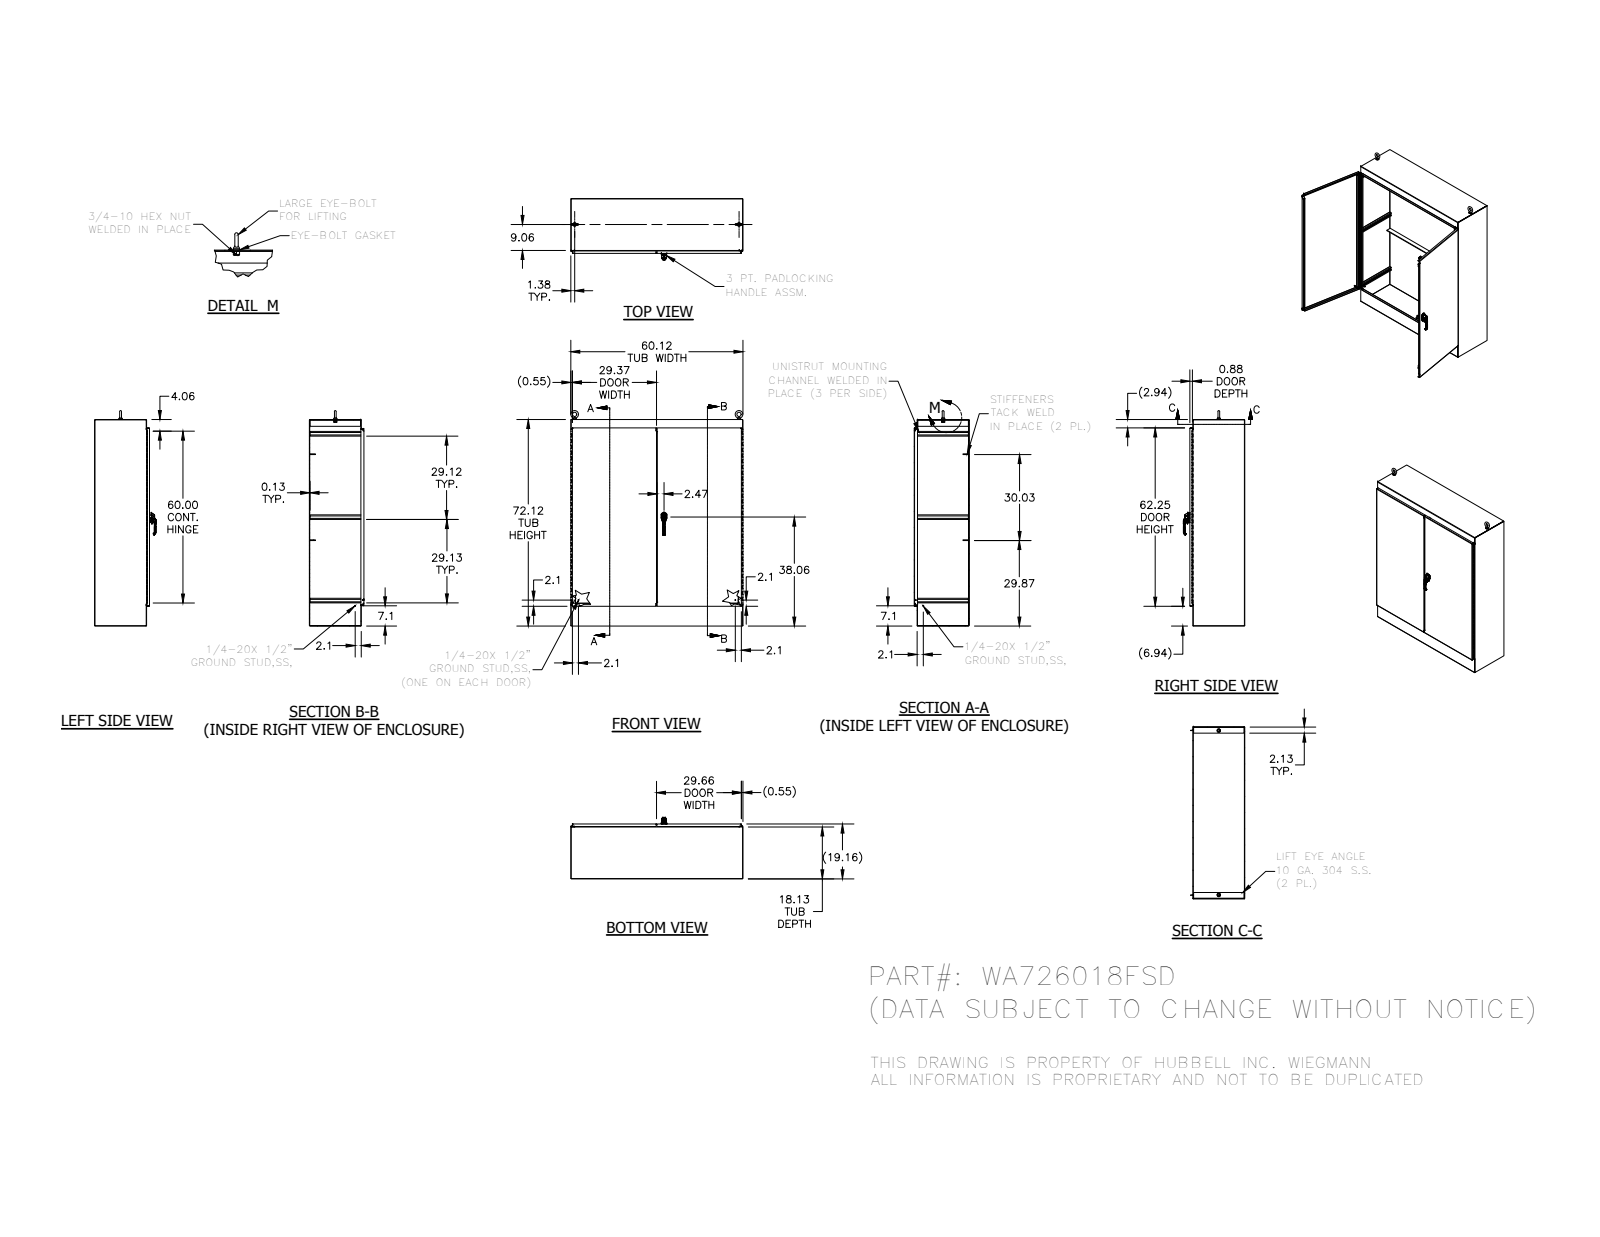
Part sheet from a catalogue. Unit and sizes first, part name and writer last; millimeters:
Units: millimetres
Overall size (bounding box): 1911.29 × 1527.54 × 544.36
Round holes (diameter × count): ⌀7.02 ×8, ⌀5.08 ×4, ⌀5.4 ×3, ⌀6 ×3, ⌀7.11 ×3, ⌀3.17 ×2, ⌀6.13 ×2, ⌀6.35 ×2, ⌀6.41 ×2, ⌀10.16 ×2, ⌀10.33 ×2, ⌀10.5 ×2
Round bosses / shafts (diameter × count): ⌀6.35 ×5, ⌀8.56 ×3, ⌀31.75 ×2, ⌀28.45 ×2, ⌀25.4 ×2, ⌀19.05 ×2, ⌀14.29 ×2, ⌀13.37 ×2
Partial cylindrical surfaces — rounded edges, fillets, slot ends (radius × count): R0.5 ×164, R0.3 ×84, R0.79 ×24, R3.97 ×21, R0.47 ×19, R0.25 ×16, R2 ×15, R1.27 ×14
Main face-to-face distances: 3.18, 3.17, 483.57, 480.39, 486.74, 483.56, 1524, 1828.8, 457.2, 1520.82
Hole centre spacings: 6, 6.5, 9.67, 9.69, 9.72, 12.49, 12.5, 19.36
Volume: 32 380 000 mm³ · Surface area: 20 400 000 mm²
Bodies: 66 solids, 3780 faces (1777 planar, 1263 cylindrical, 740 other)
Part name (STEP PRODUCT): FUN00101; HFW3025; 316298; 349132 (+8 more)
STEP written by: Autodesk Inventor 2014 (AUTOMOTIVE_DESIGN)
